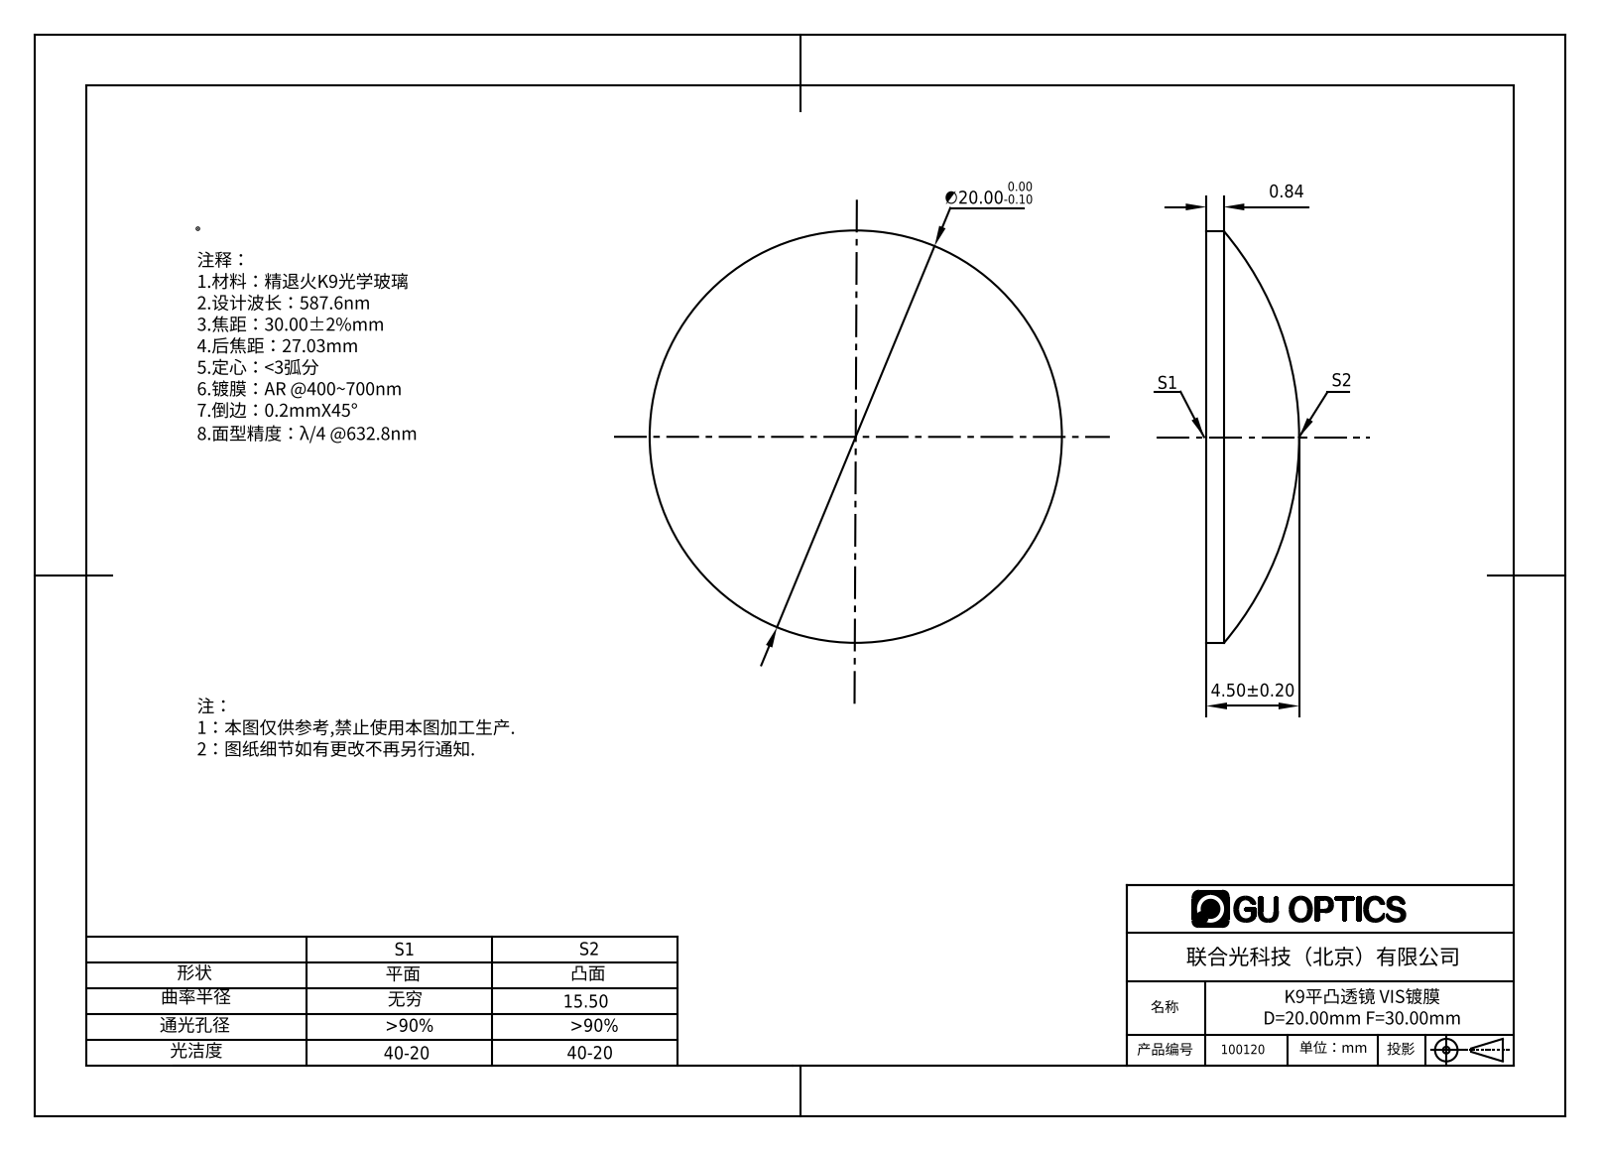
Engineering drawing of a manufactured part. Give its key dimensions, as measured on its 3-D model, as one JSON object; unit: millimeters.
{"part_name": "100120", "step_written_by": "SolidWorks 2016 (AUTOMOTIVE_DESIGN)", "units": "millimeters", "bodies": {"solids": 1, "faces": 5, "planar": 1, "cylindrical": 2, "other": 2}, "overall_size": [20, 20, 4.5], "volume_mm3": 865, "surface_area_mm2": 723, "round_bosses_or_shafts": [[20, 1]]}
